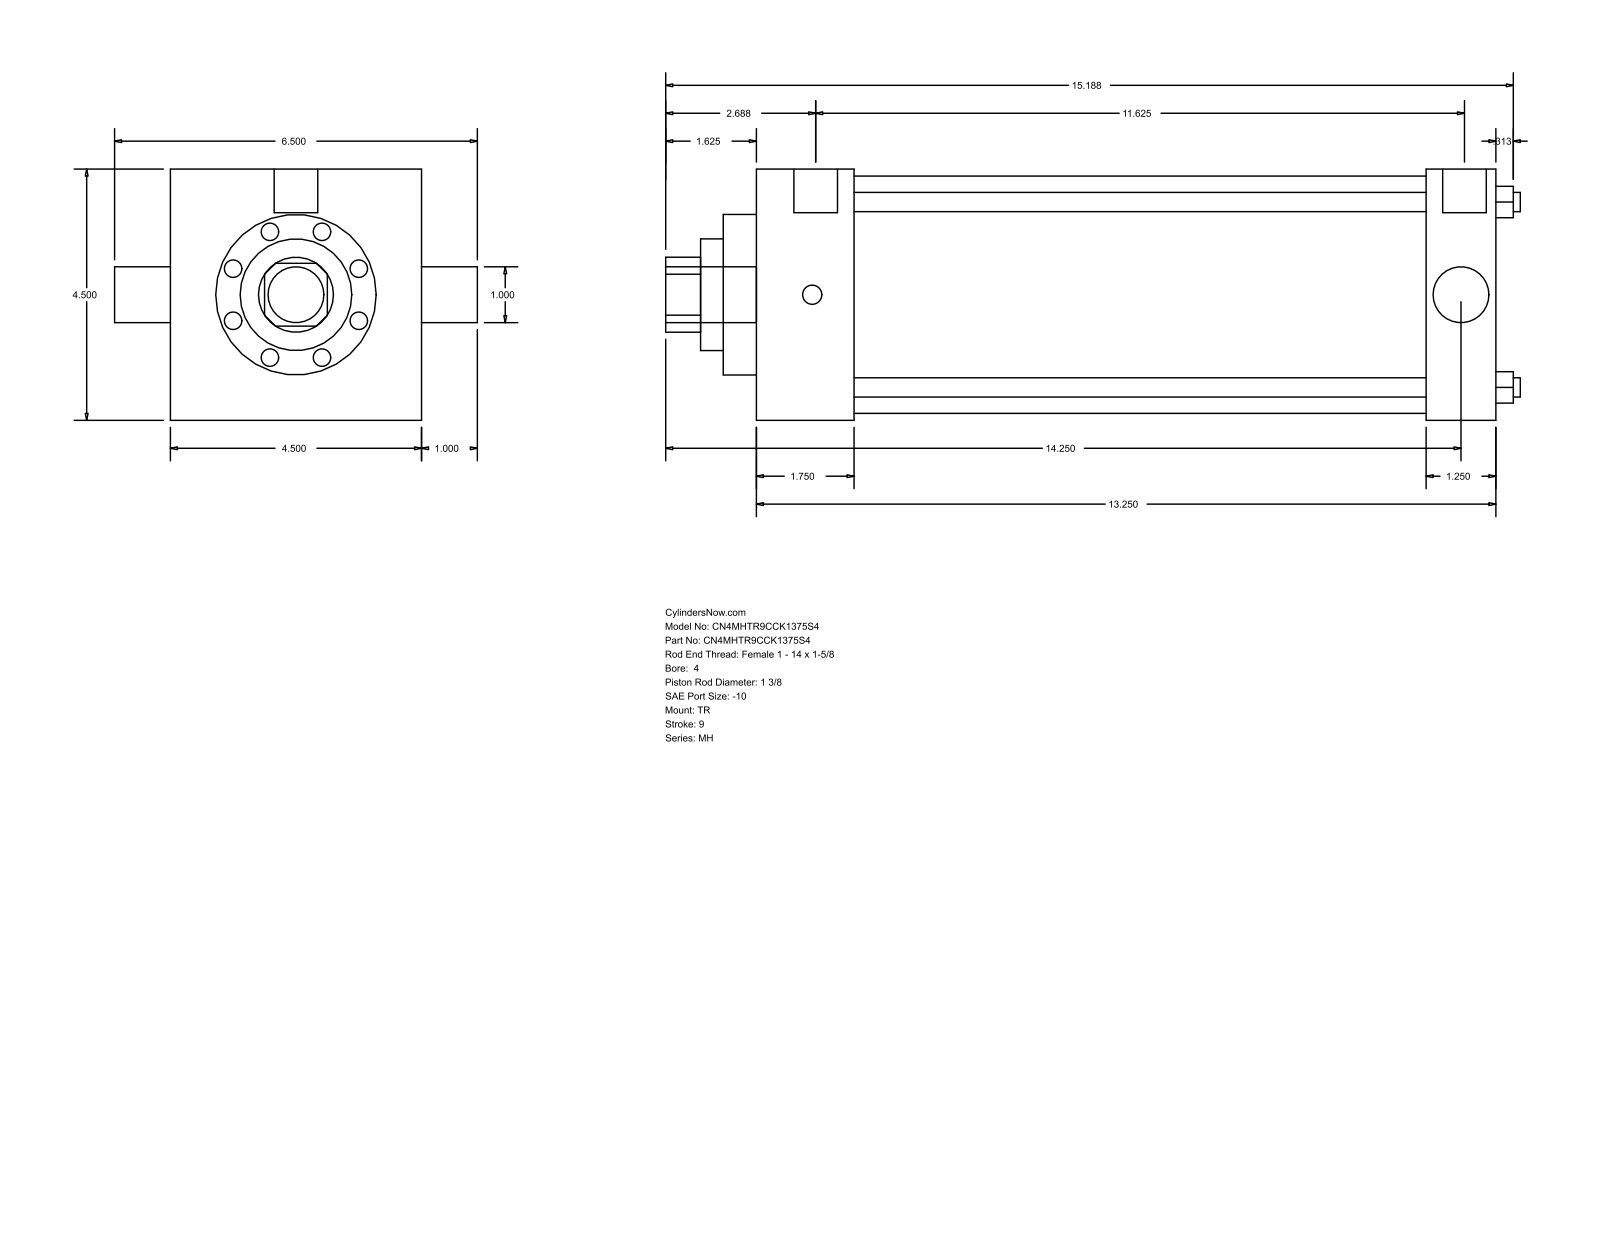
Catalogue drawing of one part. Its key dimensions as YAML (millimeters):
part_name: "MH_TR__0400_1.375"
step_written_by: "GSSL Pune (CONFIG_CONTROL_DESIGN)"
units: millimeters
bodies: {solids: 0, faces: 86, planar: 61, cylindrical: 25, other: 0}
overall_size: [388.94, 165.1, 114.3]
round_holes:
  - {diameter: 8.76, count: 4}
  - {diameter: 25.4, count: 1}
  - {diameter: 34.92, count: 1}
  - {diameter: 50.8, count: 1}
  - {diameter: 73.03, count: 1}
  - {diameter: 107.95, count: 1}
round_bosses_or_shafts:
  - {diameter: 8.73, count: 3}
  - {diameter: 19.84, count: 2}
  - {diameter: 25.4, count: 1}
partial_cylinders:
  - {radius: 17.06, count: 1}
face_to_face_distances: [114.3, 336.55, 44.45, 292.1, 304.8, 260.35, 31.75, 15.08, 59.53, 319.88]
hole_center_spacings: [59.62, 84.32, 119.25]
